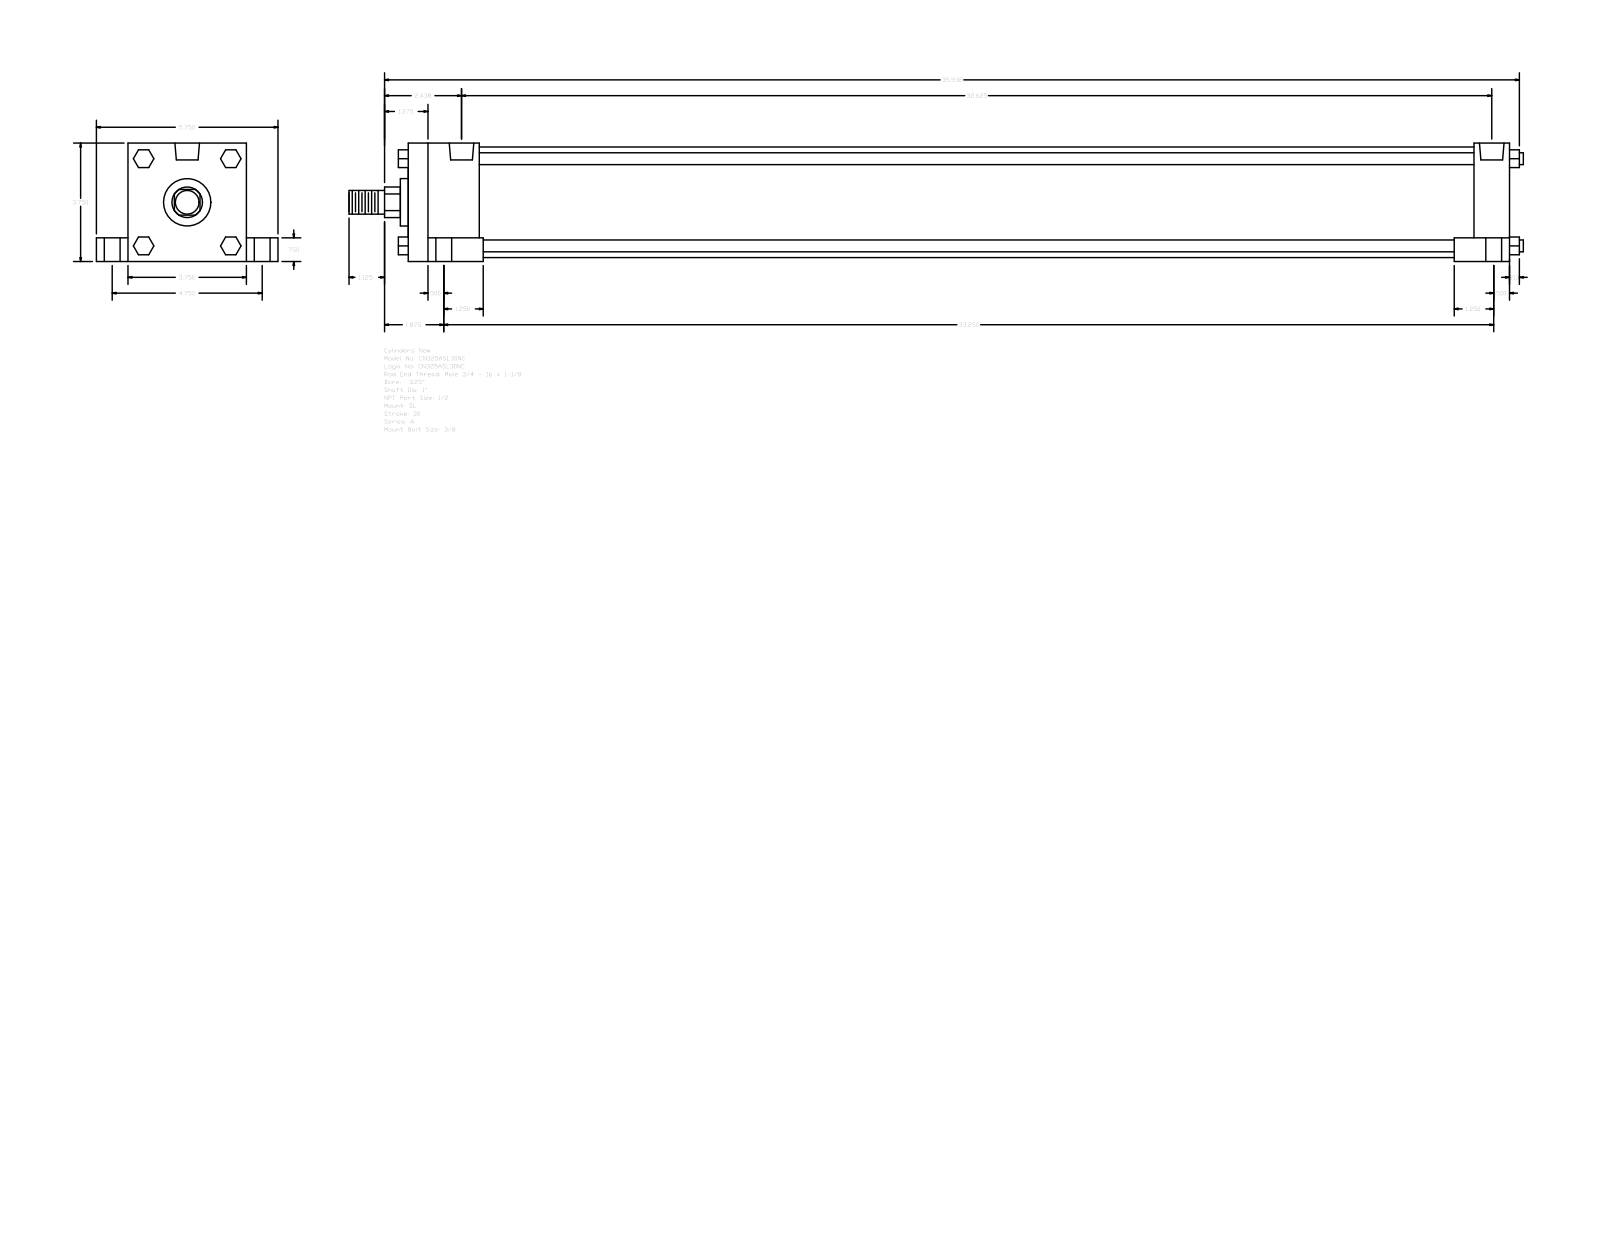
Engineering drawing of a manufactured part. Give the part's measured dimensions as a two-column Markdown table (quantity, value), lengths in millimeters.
| quantity | value |
| --- | --- |
| part name | A_SL__0325_1 |
| STEP written by | GSSL Pune (CONFIG_CONTROL_DESIGN) |
| units | millimeters |
| bodies | 0 solids, 150 faces (114 planar, 36 cylindrical, 0 other) |
| overall size | 944.56 × 146.05 × 95.25 |
| round holes (diameter × count) | 8.73 × 4, 12.7 × 4, 19.05 × 4, 19.77 × 2 |
| round bosses / shafts (diameter × count) | 9.53 × 4, 88.9 × 1, 38.1 × 1, 25.4 × 1, 19.05 × 1 |
| partial cylindrical surfaces (radius × count) | 12.29 × 1 |
| main face-to-face distances | 95.24, 885.83, 19.05, 25.41, 120.65, 76.19, 57.15, 857.25, 800.1, 828.68 |
| hole center spacings | 3.18, 60.35, 60.52, 62, 62.81, 120.66, 822.32, 825.5 |
